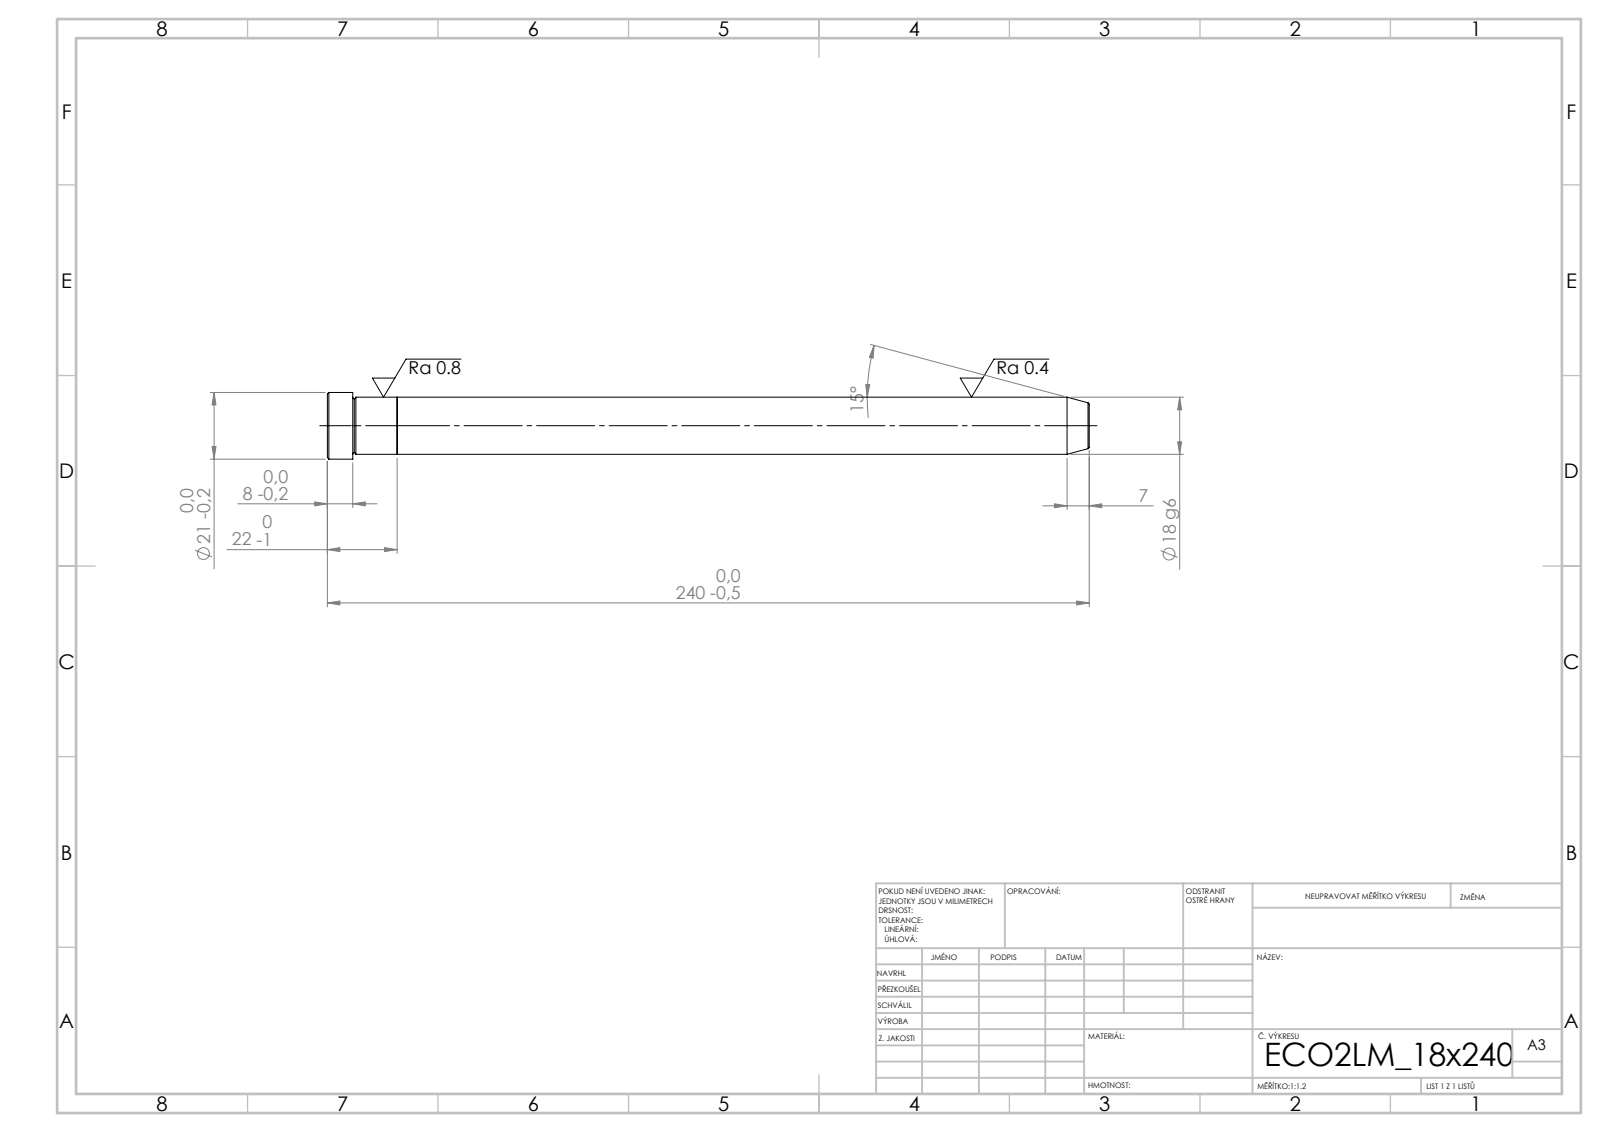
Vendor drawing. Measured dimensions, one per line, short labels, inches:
written by: SolidWorks 2019 (CONFIG_CONTROL_DESIGN)
unit: in
bodies: 2 solids, 21 faces (5 planar, 6 cylindrical, 10 other)
size: 9.449 × 0.827 × 0.827
volume: 3.749 in³; area: 22.83 in²
bosses: 1× ⌀0.827, 1× ⌀0.709
face distances: 0.866, 8.583, 9.449, 9.134, 0.551, 0.315
